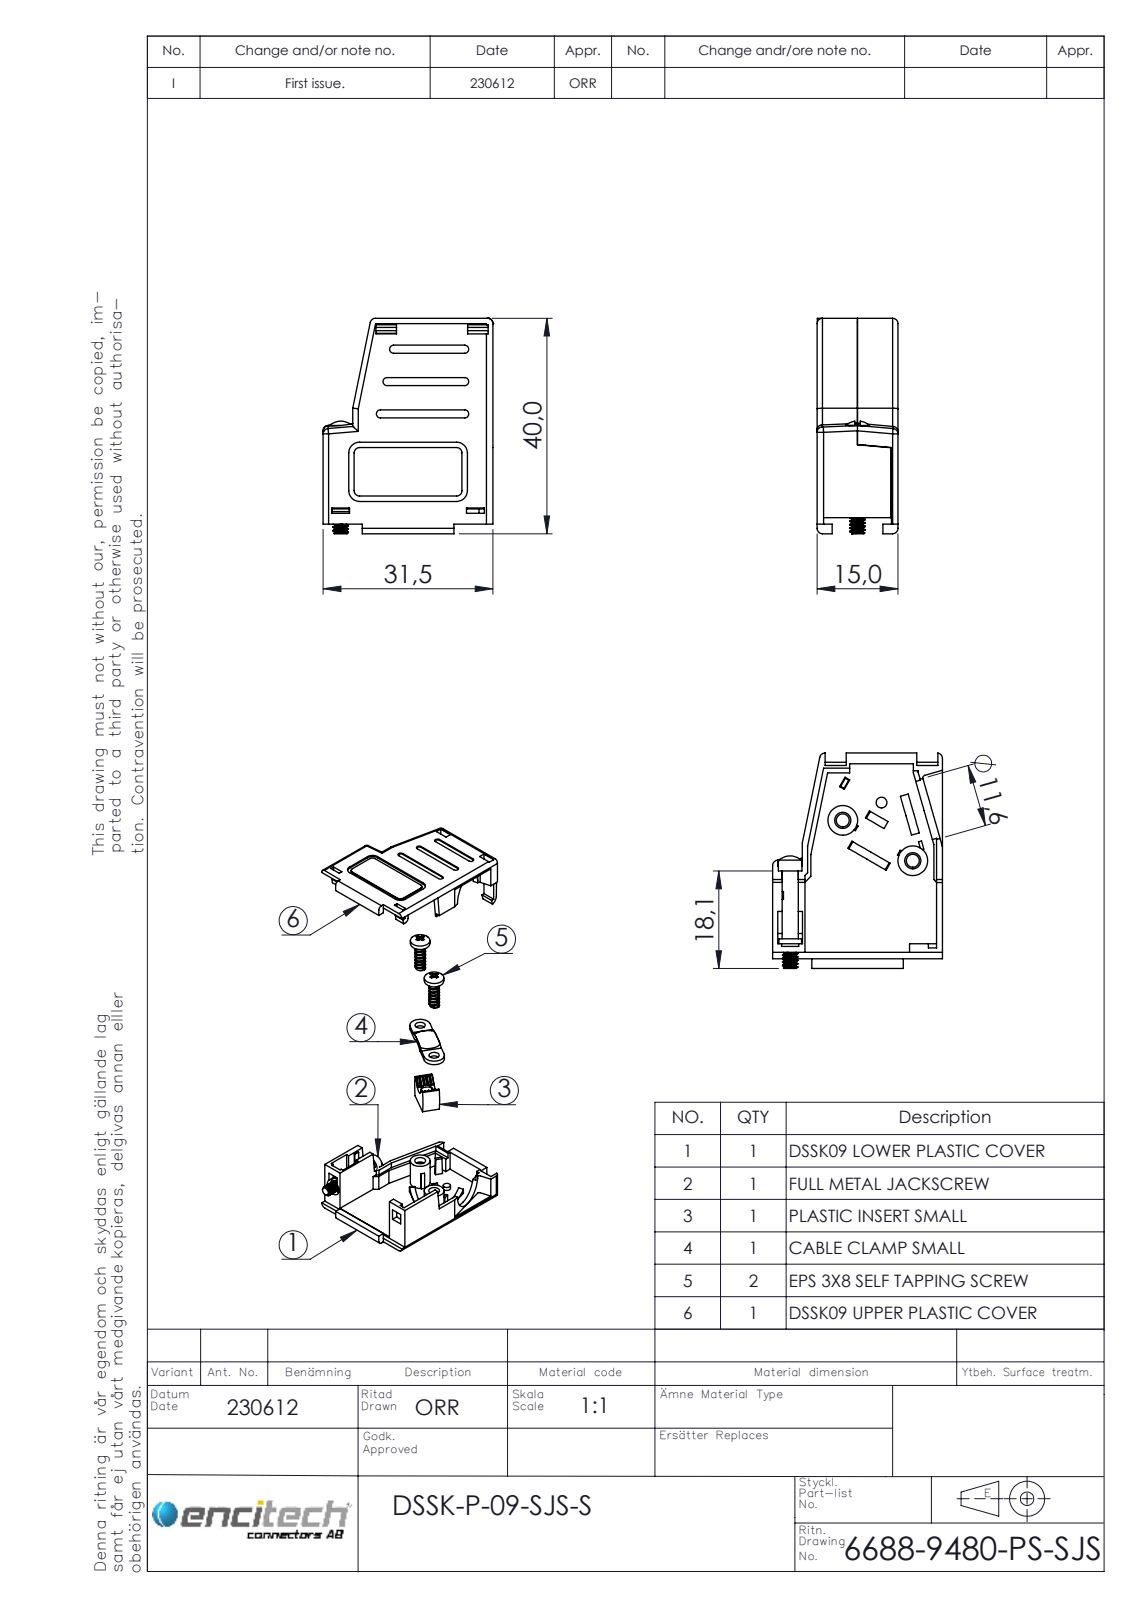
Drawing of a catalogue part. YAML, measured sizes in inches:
part_name: "6811-0141-12 Part 2; 6830-0106-01; 6826-0133-01; 6688-9480-PS-SJS (+3 more)"
step_written_by: "SolidWorks 2021 (AUTOMOTIVE_DESIGN)"
units: inches
bodies: {solids: 9, faces: 629, planar: 413, cylindrical: 166, other: 50}
overall_size: [1.575, 1.24, 0.591]
volume: 0.403
surface_area: 15.4
round_holes:
  - {diameter: 0.118, count: 3}
  - {diameter: 0.094, count: 2}
  - {diameter: 0.11, count: 2}
  - {diameter: 0.138, count: 1}
  - {diameter: 0.177, count: 1}
  - {diameter: 0.457, count: 1}
round_bosses_or_shafts:
  - {diameter: 0.217, count: 2}
  - {diameter: 0.215, count: 2}
  - {diameter: 0.097, count: 2}
  - {diameter: 0.173, count: 1}
  - {diameter: 0.165, count: 1}
  - {diameter: 0.112, count: 1}
  - {diameter: 0.079, count: 1}
partial_cylinders:
  - {radius: 0.039, count: 21}
  - {radius: 0.03, count: 6}
  - {radius: 0.079, count: 6}
  - {radius: 0.02, count: 5}
  - {radius: 0.047, count: 3}
  - {radius: 0.112, count: 2}
  - {radius: 0.512, count: 2}
  - {radius: 0.091, count: 1}
face_to_face_distances: [0.067, 0.524, 0.457, 0.591, 0.059, 0.047, 0.228, 0.295, 0.287, 0.043]
hole_center_spacings: [0.294, 0.296, 0.591]
